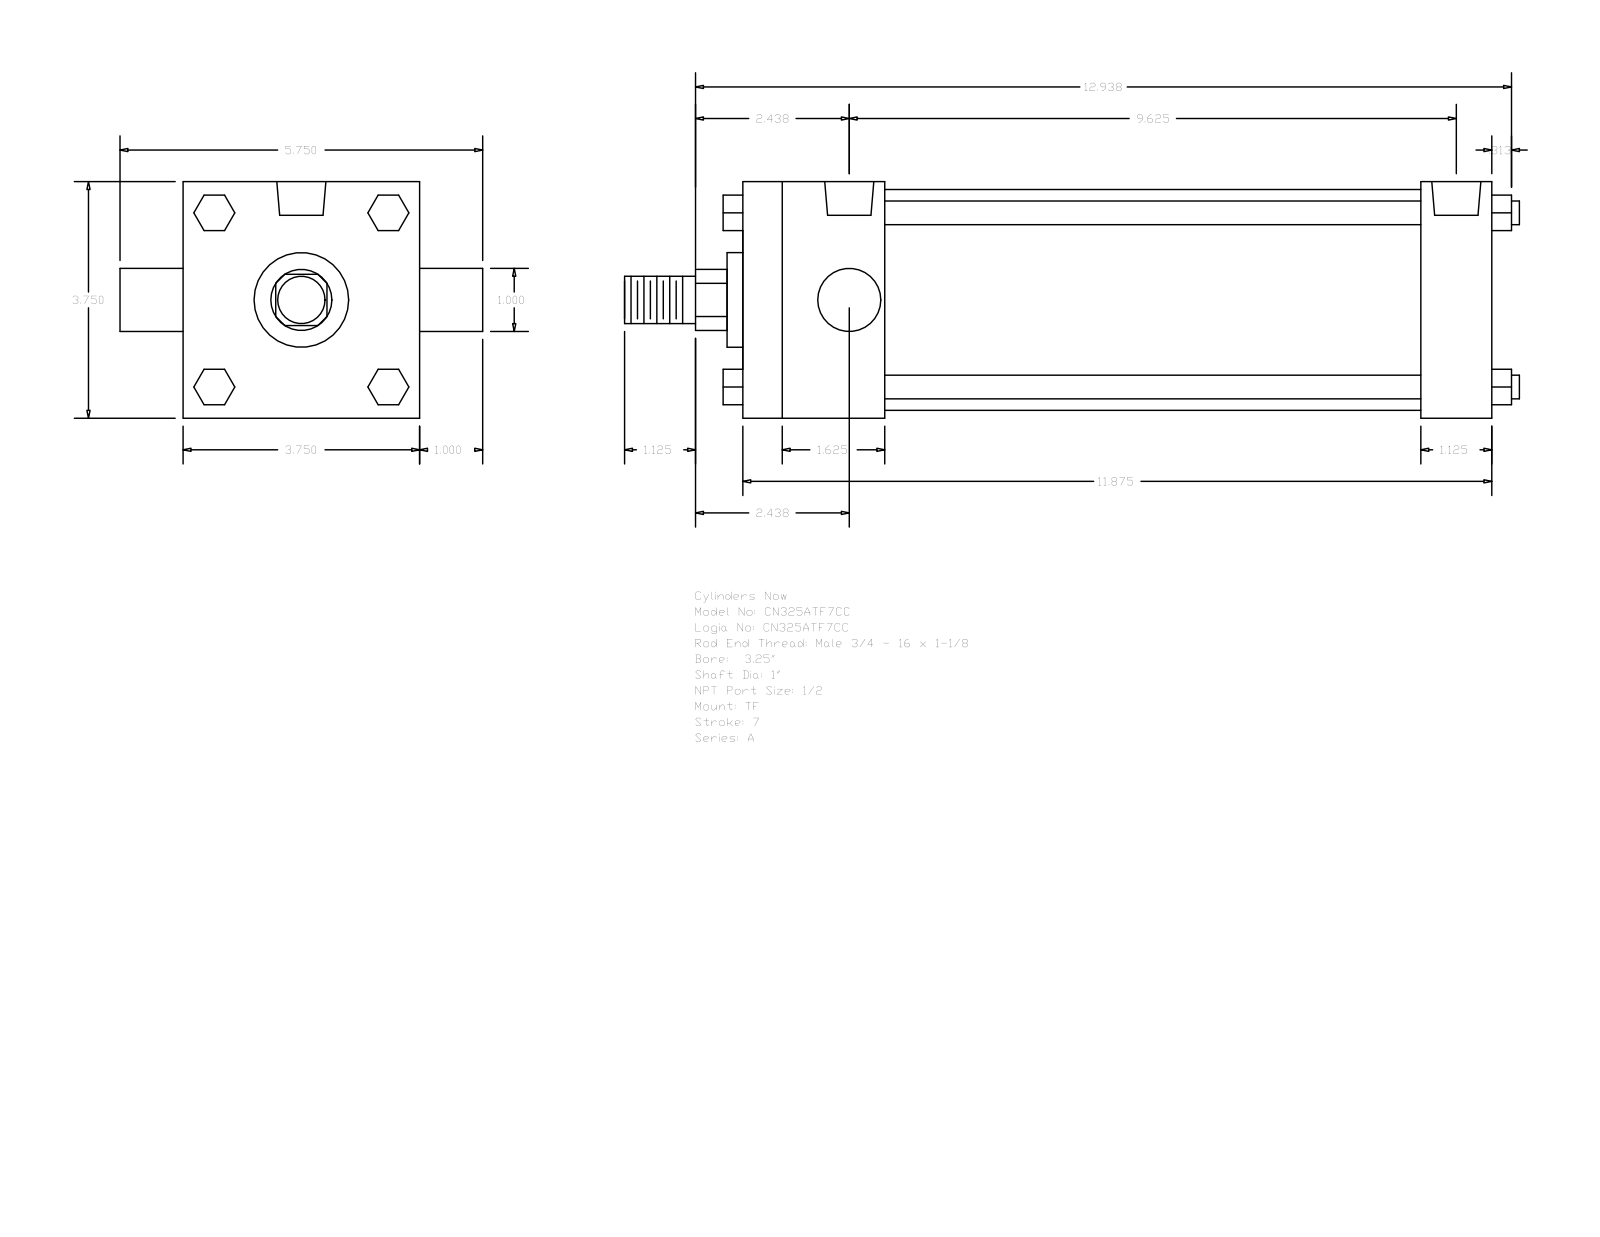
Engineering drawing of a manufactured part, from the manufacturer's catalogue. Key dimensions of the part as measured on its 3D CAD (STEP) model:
Part name (STEP PRODUCT): A_TF__0325_1
STEP written by: GSSL Pune (CONFIG_CONTROL_DESIGN)
Units: millimetres
Bodies: 0 solids, 120 faces (92 planar, 28 cylindrical, 0 other)
Overall size (bounding box): 360.36 × 146.05 × 95.25
Round holes (diameter × count): ⌀8.73 ×3, ⌀19.77 ×2
Round bosses / shafts (diameter × count): ⌀9.53 ×4, ⌀25.4 ×2, ⌀88.9 ×1, ⌀38.1 ×1, ⌀19.05 ×1
Partial cylindrical surfaces — rounded edges, fillets, slot ends (radius × count): R12.29 ×1
Main face-to-face distances: 95.24, 301.63, 57.15, 273.05, 215.9, 244.48, 28.58, 14.28, 35.05, 60.71
Hole centre spacings: 3.18, 241.3, 238.12, 244.48
